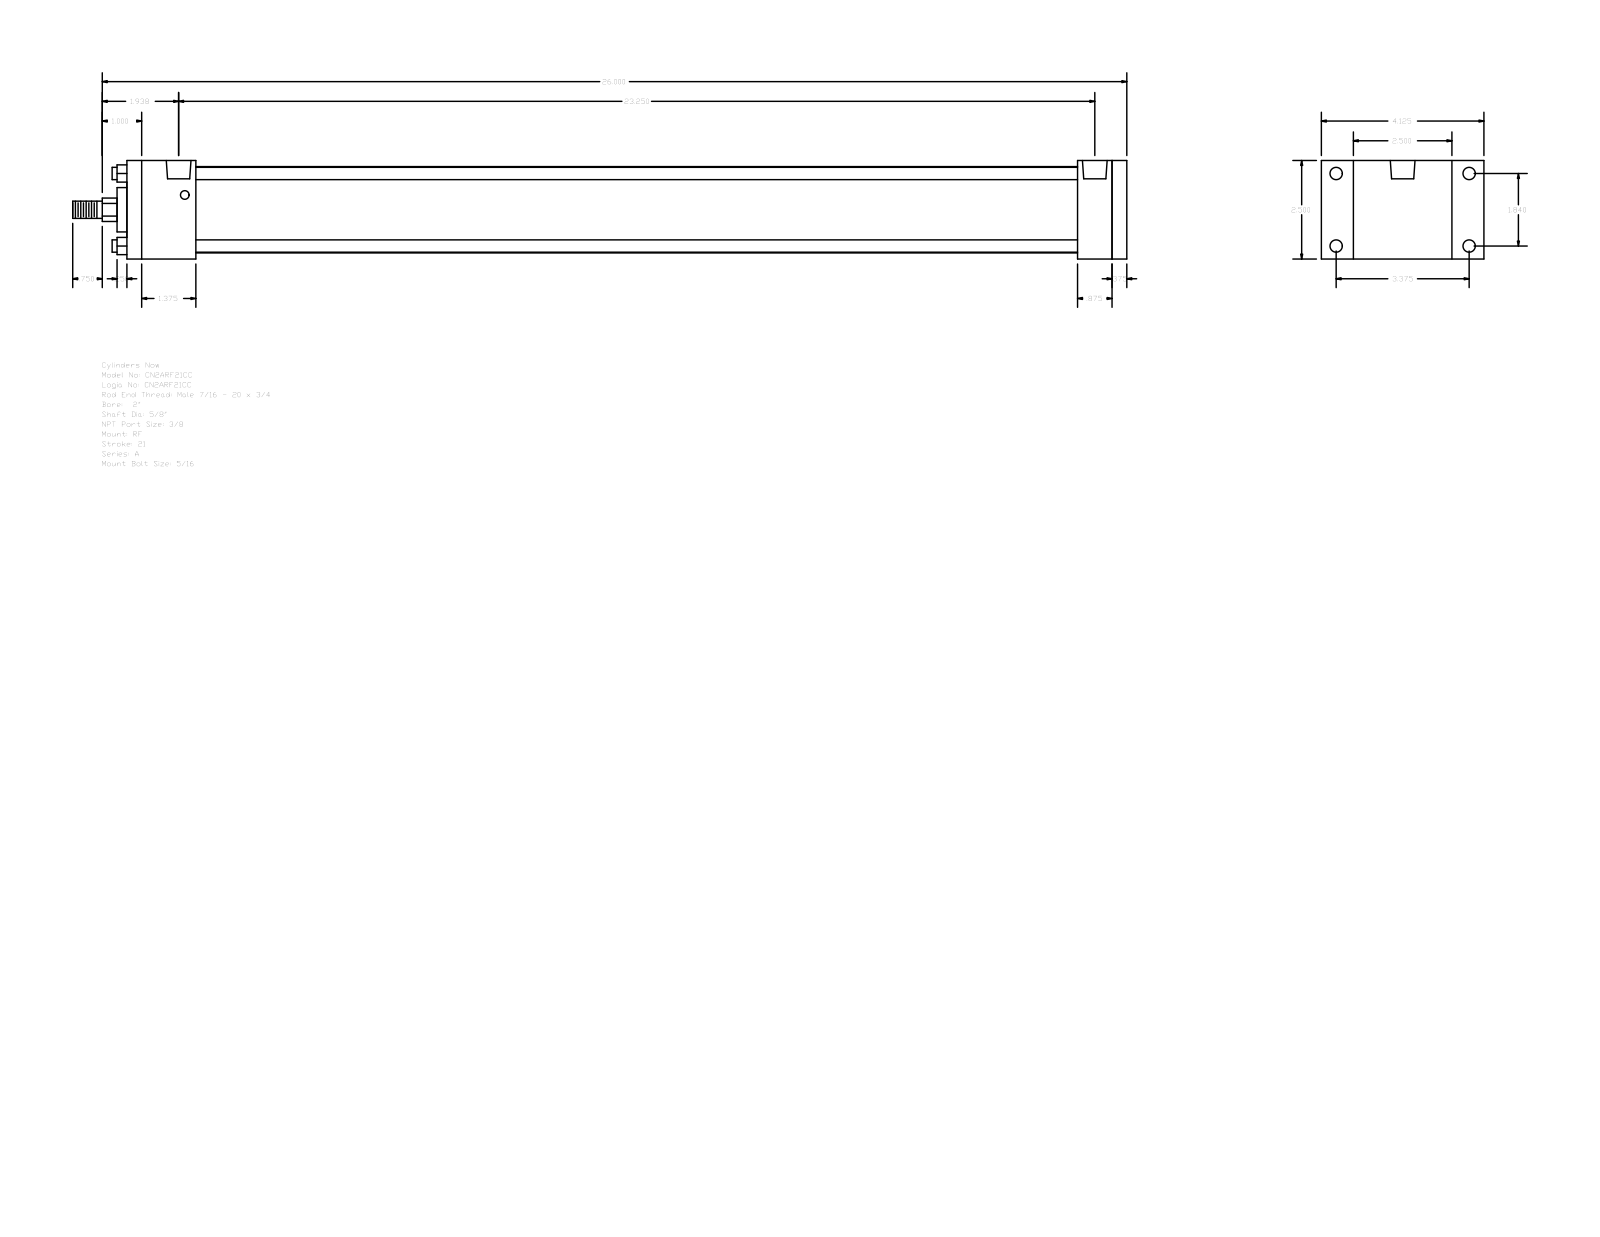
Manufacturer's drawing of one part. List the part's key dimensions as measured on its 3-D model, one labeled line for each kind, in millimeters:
Part name (STEP PRODUCT): A_RF__0200_0.625
STEP written by: GSSL Pune (CONFIG_CONTROL_DESIGN)
Units: millimetres
Bodies: 0 solids, 92 faces (64 planar, 28 cylindrical, 0 other)
Overall size (bounding box): 679.45 × 104.78 × 63.5
Round holes (diameter × count): ⌀5.56 ×4, ⌀7.94 ×4, ⌀15.93 ×2
Round bosses / shafts (diameter × count): ⌀7.94 ×4, ⌀55.63 ×1, ⌀28.57 ×1, ⌀15.88 ×1, ⌀11.11 ×1
Partial cylindrical surfaces — rounded edges, fillets, slot ends (radius × count): R7.54 ×1
Main face-to-face distances: 63.5, 644.52, 635, 9.52, 44.45, 590.55, 600.07, 612.77, 568.32, 22.23
Hole centre spacings: 46.74, 85.72, 97.63, 582.6, 3.97, 3.98, 586.57, 586.58
